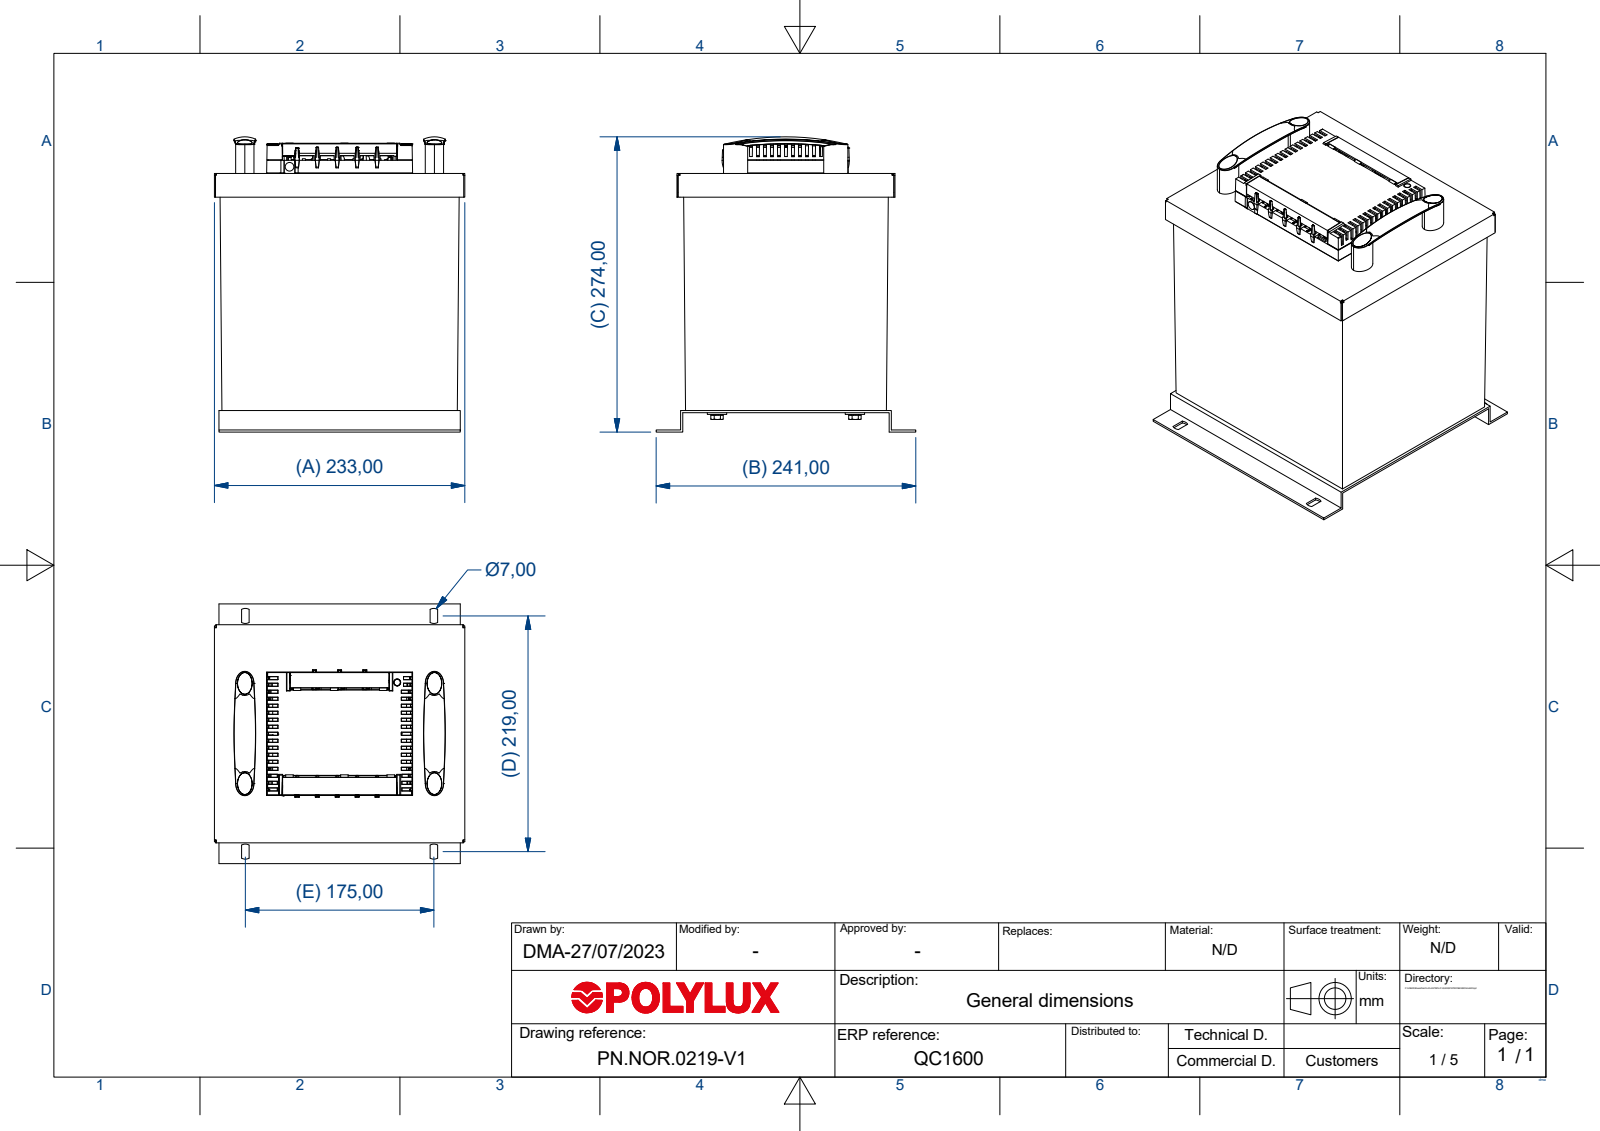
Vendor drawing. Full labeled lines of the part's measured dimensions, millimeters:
Part name (STEP PRODUCT): RC64x90Q
STEP written by: Autodesk Inventor 2018 (AUTOMOTIVE_DESIGN)
Units: millimetres
Bodies: 0 solids, 1460 faces (1032 planar, 131 cylindrical, 297 other)
Overall size (bounding box): 274 × 241 × 232.4
Round bosses / shafts (diameter × count): ⌀18 ×4, ⌀8 ×1
Partial cylindrical surfaces — rounded edges, fillets, slot ends (radius × count): R2 ×8, R0.5 ×7, R0.2 ×6, R4.35 ×4, R5.5 ×4, R7 ×4, R820 ×2, R0.15 ×1
Main face-to-face distances: 1, 2, 219, 220, 221, 222, 18, 20, 239, 240
